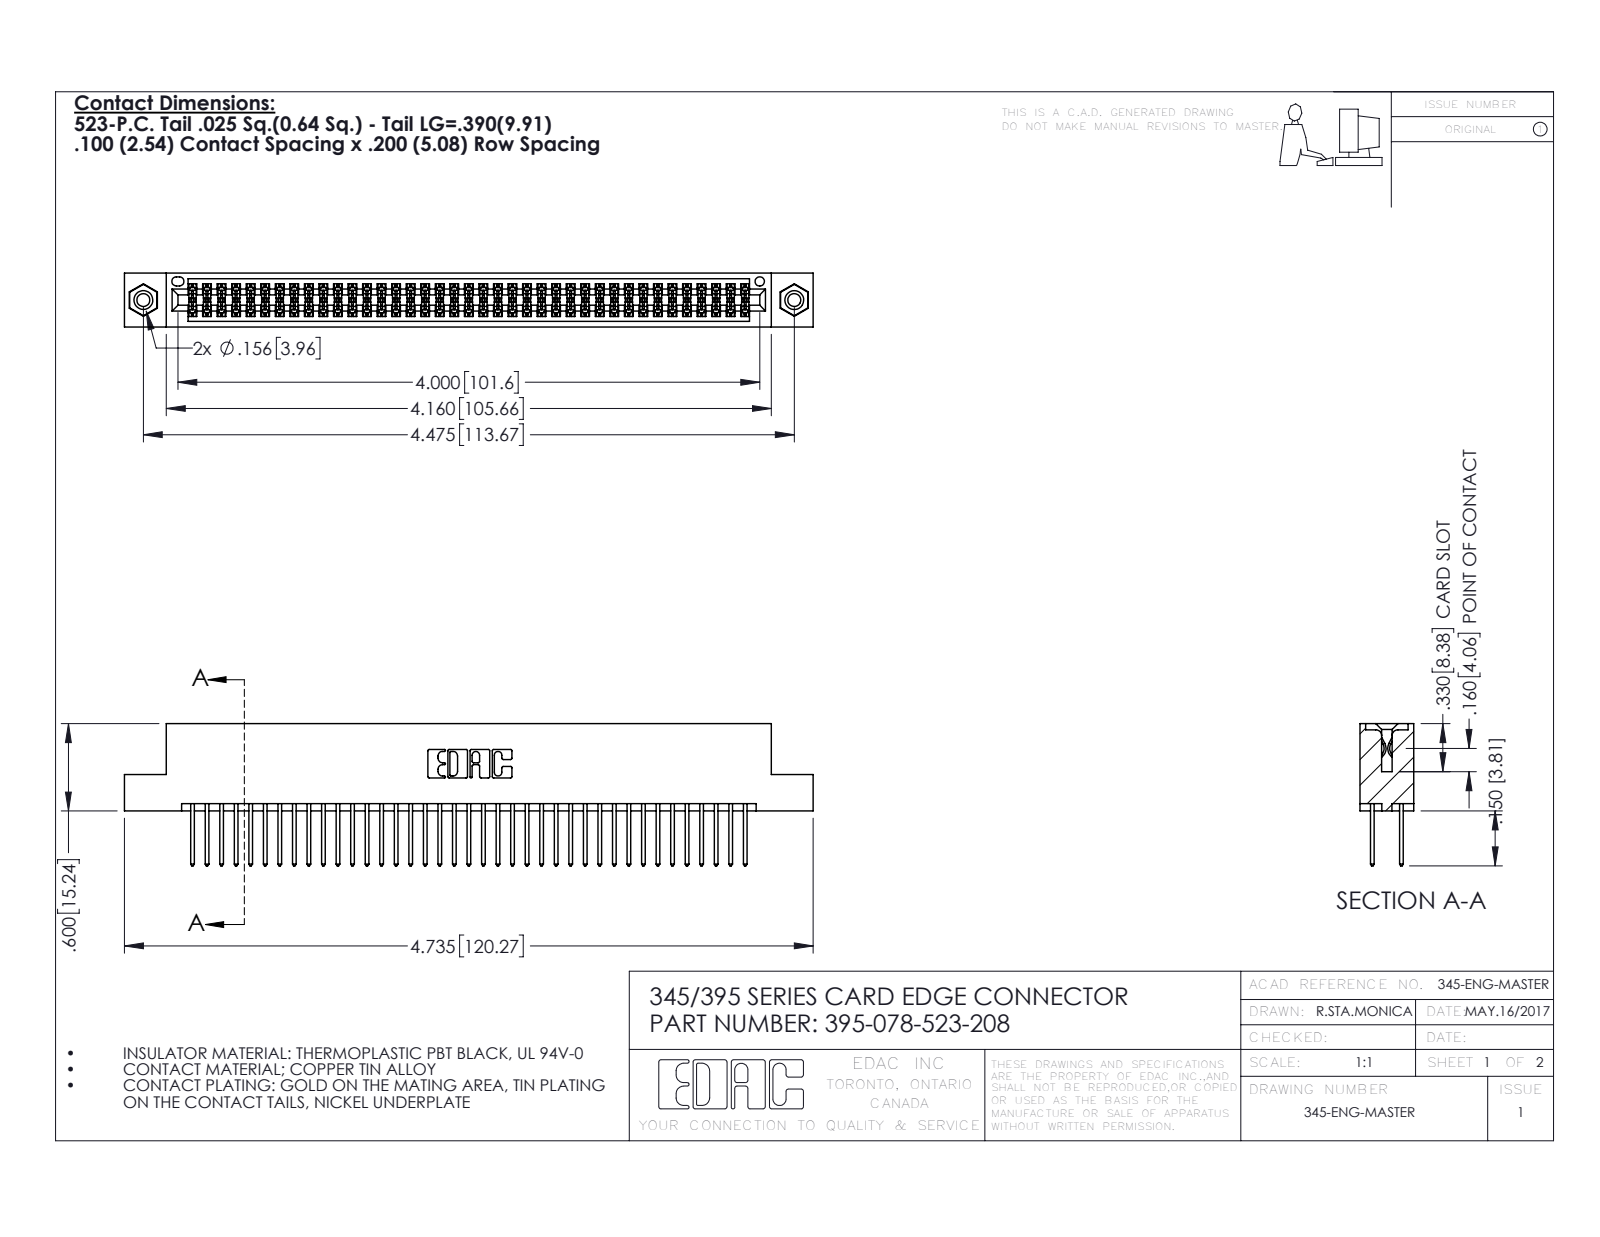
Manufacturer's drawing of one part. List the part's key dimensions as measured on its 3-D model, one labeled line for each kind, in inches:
Part name (STEP PRODUCT): 345 Part_Flush Mounting Lugs - 0.156 Dia-TI; 345-250-001_345-250-003-102; 345-292-001_345-293-123; 395-078-523-208
STEP written by: SolidWorks 2016 (CONFIG_CONTROL_DESIGN)
Units: inches
Bodies: 81 solids, 4086 faces (2686 planar, 1384 cylindrical, 16 other)
Overall size (bounding box): 4.735 × 0.977 × 0.37
Volume: 0.721 in³ · Surface area: 28.1 in²
Round holes (diameter × count): ⌀0.089 ×2, ⌀0.125 ×2, ⌀0.156 ×2, ⌀0.064 ×1
Round bosses / shafts (diameter × count): ⌀0.155 ×2
Partial cylindrical surfaces — rounded edges, fillets, slot ends (radius × count): R0.006 ×117, R0.01 ×78, R0.01 ×22, R0.007 ×6, R0.031 ×6, R0.026 ×3, R0.014 ×2, R0.019 ×2
Main face-to-face distances: 0.072, 0.298, 0.2, 0.098, 0.272, 0.025, 0.37, 0.225, 0.175, 0.149
Hole centre spacings: 0.27, 4.239, 4.475
